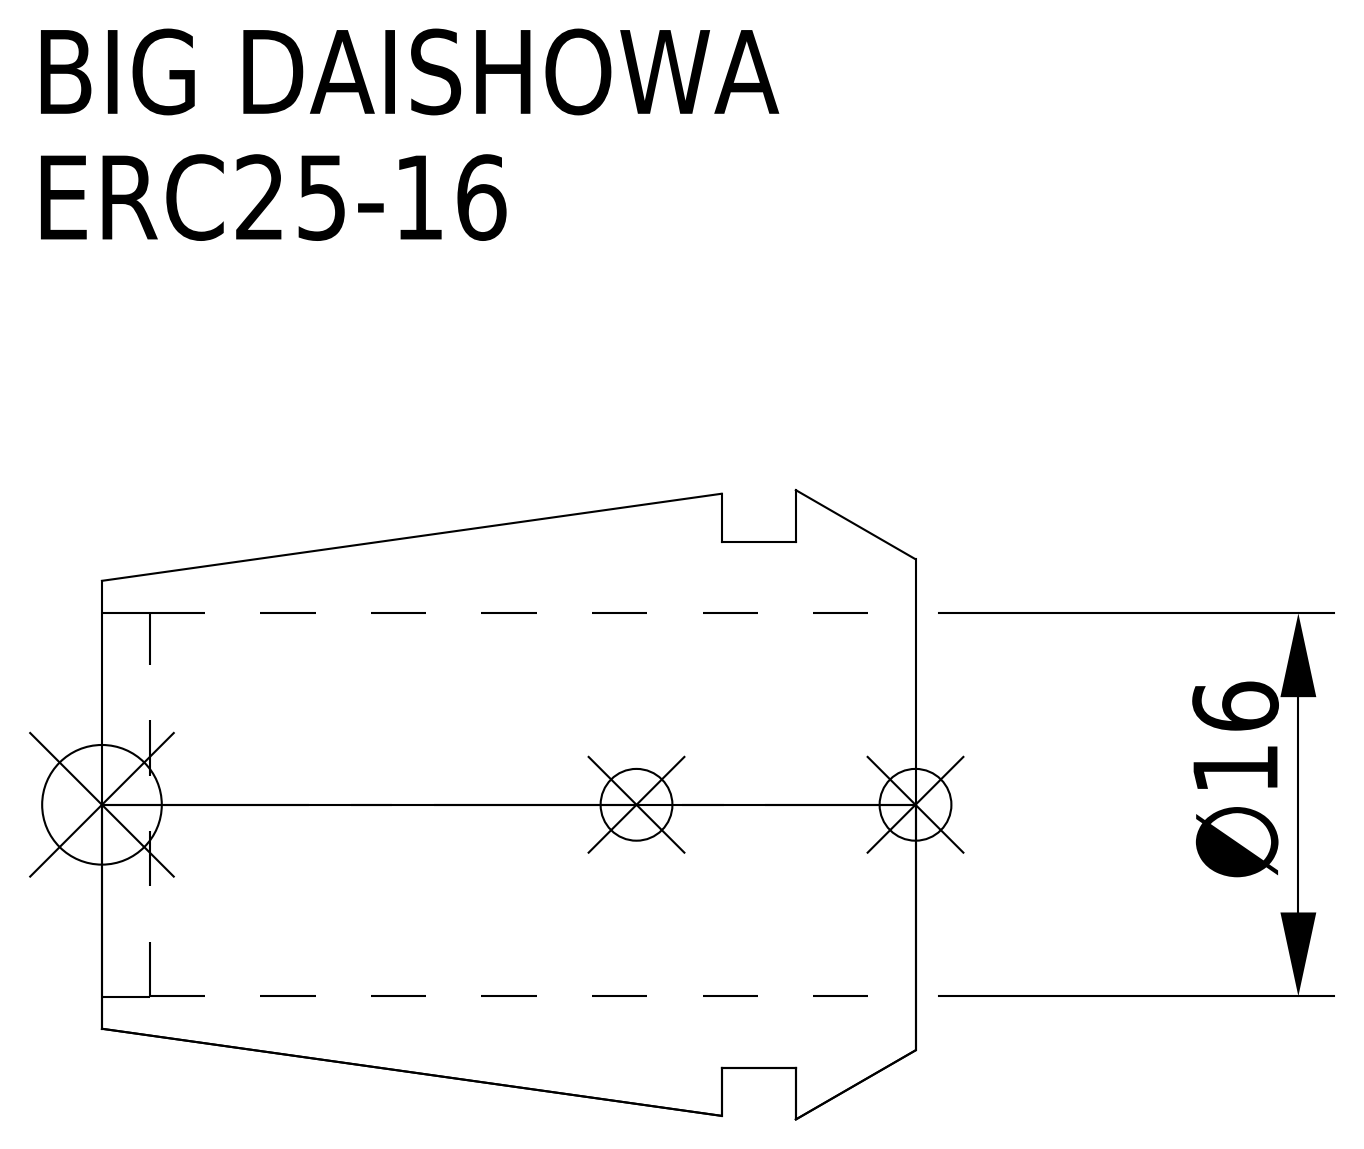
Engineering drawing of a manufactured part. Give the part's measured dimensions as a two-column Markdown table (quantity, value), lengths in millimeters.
| quantity | value |
| --- | --- |
| part name | ERC25-16 |
| STEP written by | CREO PARAMETRIC BY PTC INC, 2016380 (AUTOMOTIVE_DESIGN) |
| units | millimeters |
| bodies | 1 solid, 15 faces (5 planar, 6 cylindrical, 4 other) |
| overall size | 34 × 26.3 × 26.3 |
| volume | 6 764 mm³ |
| surface area | 4 704 mm² |
| round holes (diameter × count) | 16 × 1, 16.05 × 1 |
| round bosses / shafts (diameter × count) | 22 × 1 |
| main face-to-face distances | 3.1, 5, 8.1, 34, 29, 25.9, 32, 27, 23.9, 2 |
